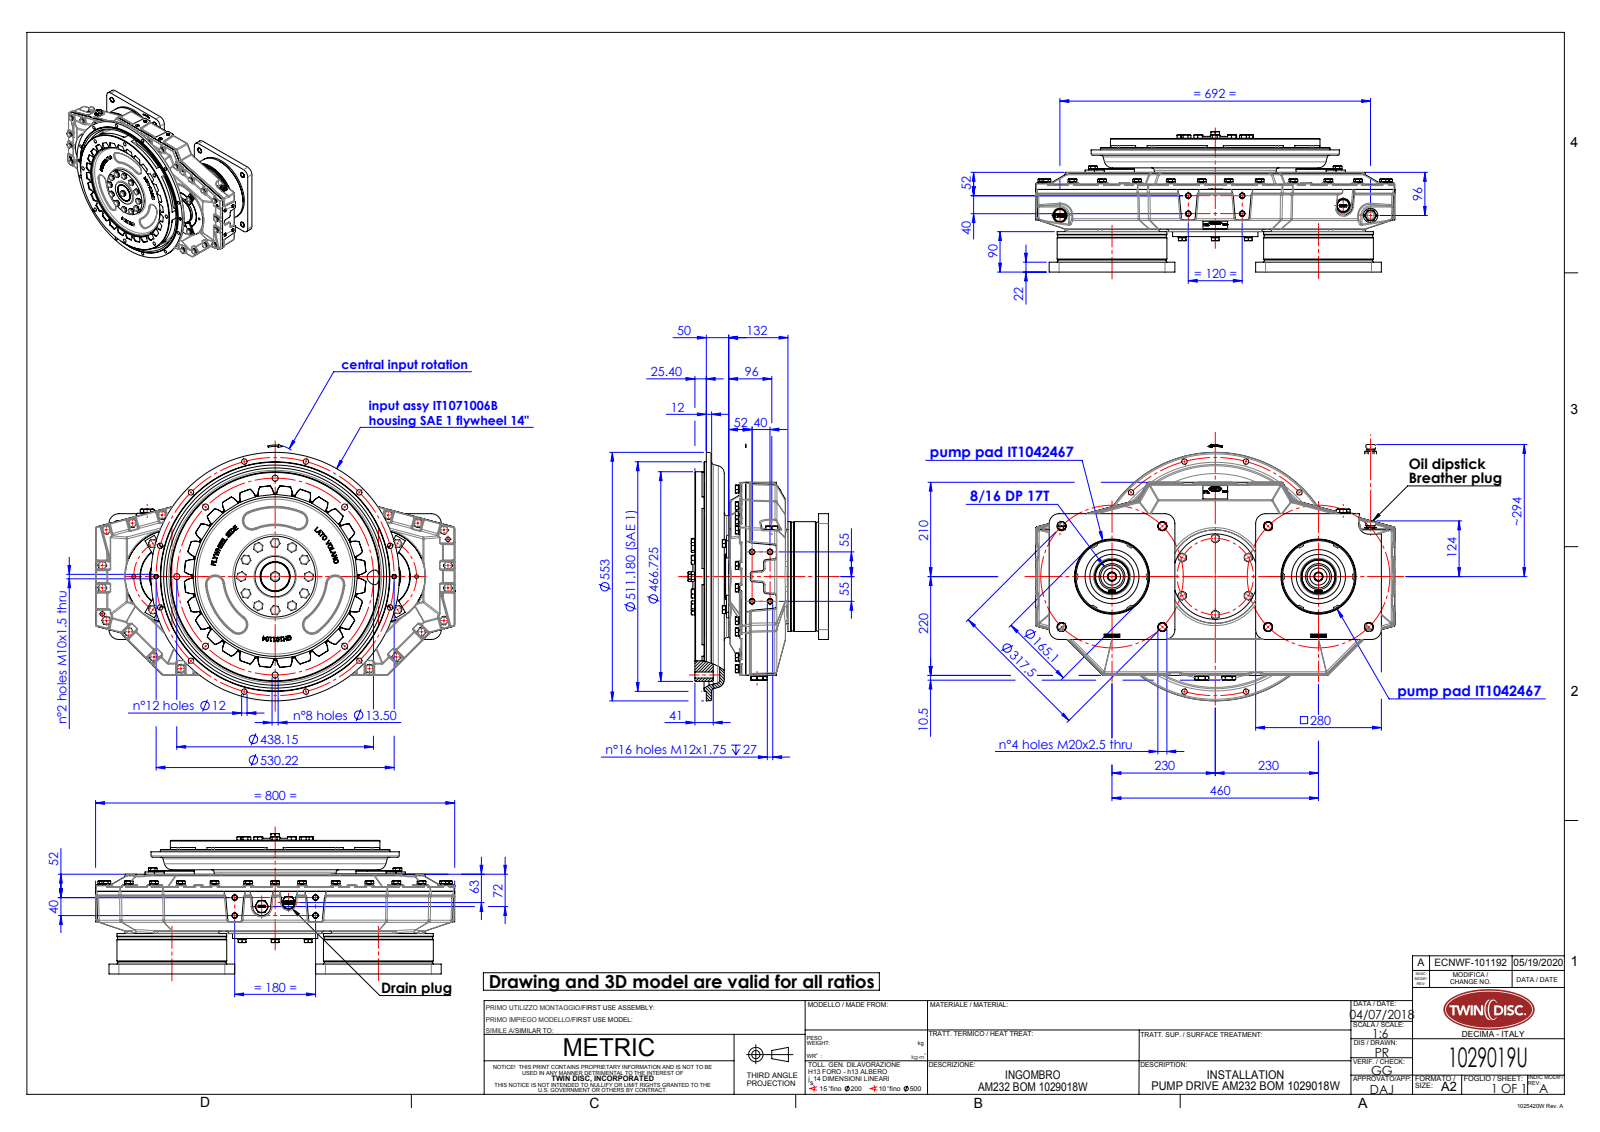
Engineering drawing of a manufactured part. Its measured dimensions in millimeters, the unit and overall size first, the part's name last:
Units: millimetres
Overall size (bounding box): 800 × 571.17 × 312.5
Round holes (diameter × count): ⌀10.2 ×66, ⌀8.5 ×32, ⌀10.5 ×29, ⌀12 ×24, ⌀13 ×20, ⌀11 ×18, ⌀10 ×10, ⌀20 ×10, ⌀13.5 ×8, ⌀17.5 ×8, ⌀12.2 ×7, ⌀21 ×4
Round bosses / shafts (diameter × count): ⌀10 ×49, ⌀18.1 ×47, ⌀16.2 ×47, ⌀18 ×19, ⌀12 ×19, ⌀24 ×12, ⌀21.1 ×7, ⌀140 ×3
Partial cylindrical surfaces — rounded edges, fillets, slot ends (radius × count): R2 ×284, R0.75 ×112, R5 ×112, R3 ×80, R2.5 ×76, R0.45 ×58, R34 ×56, R34.2 ×56
Main face-to-face distances: 10, 38, 184, 58, 48, 94, 152, 50.9, 242, 90
Hole centre spacings: 120, 57.4, 75, 138.58, 40, 150, 207.84, 30
Volume: 14 290 000 mm³ · Surface area: 4 429 000 mm²
Bodies: 28 solids, 8480 faces (3769 planar, 2287 cylindrical, 2424 other)
Part name (STEP PRODUCT): 1029019U; IT1042467_rev00-installation; IT1071006B_rev03-installation; IT0000203_rev00-installation (+6 more)
STEP written by: SolidWorks 2019 (AUTOMOTIVE_DESIGN)
